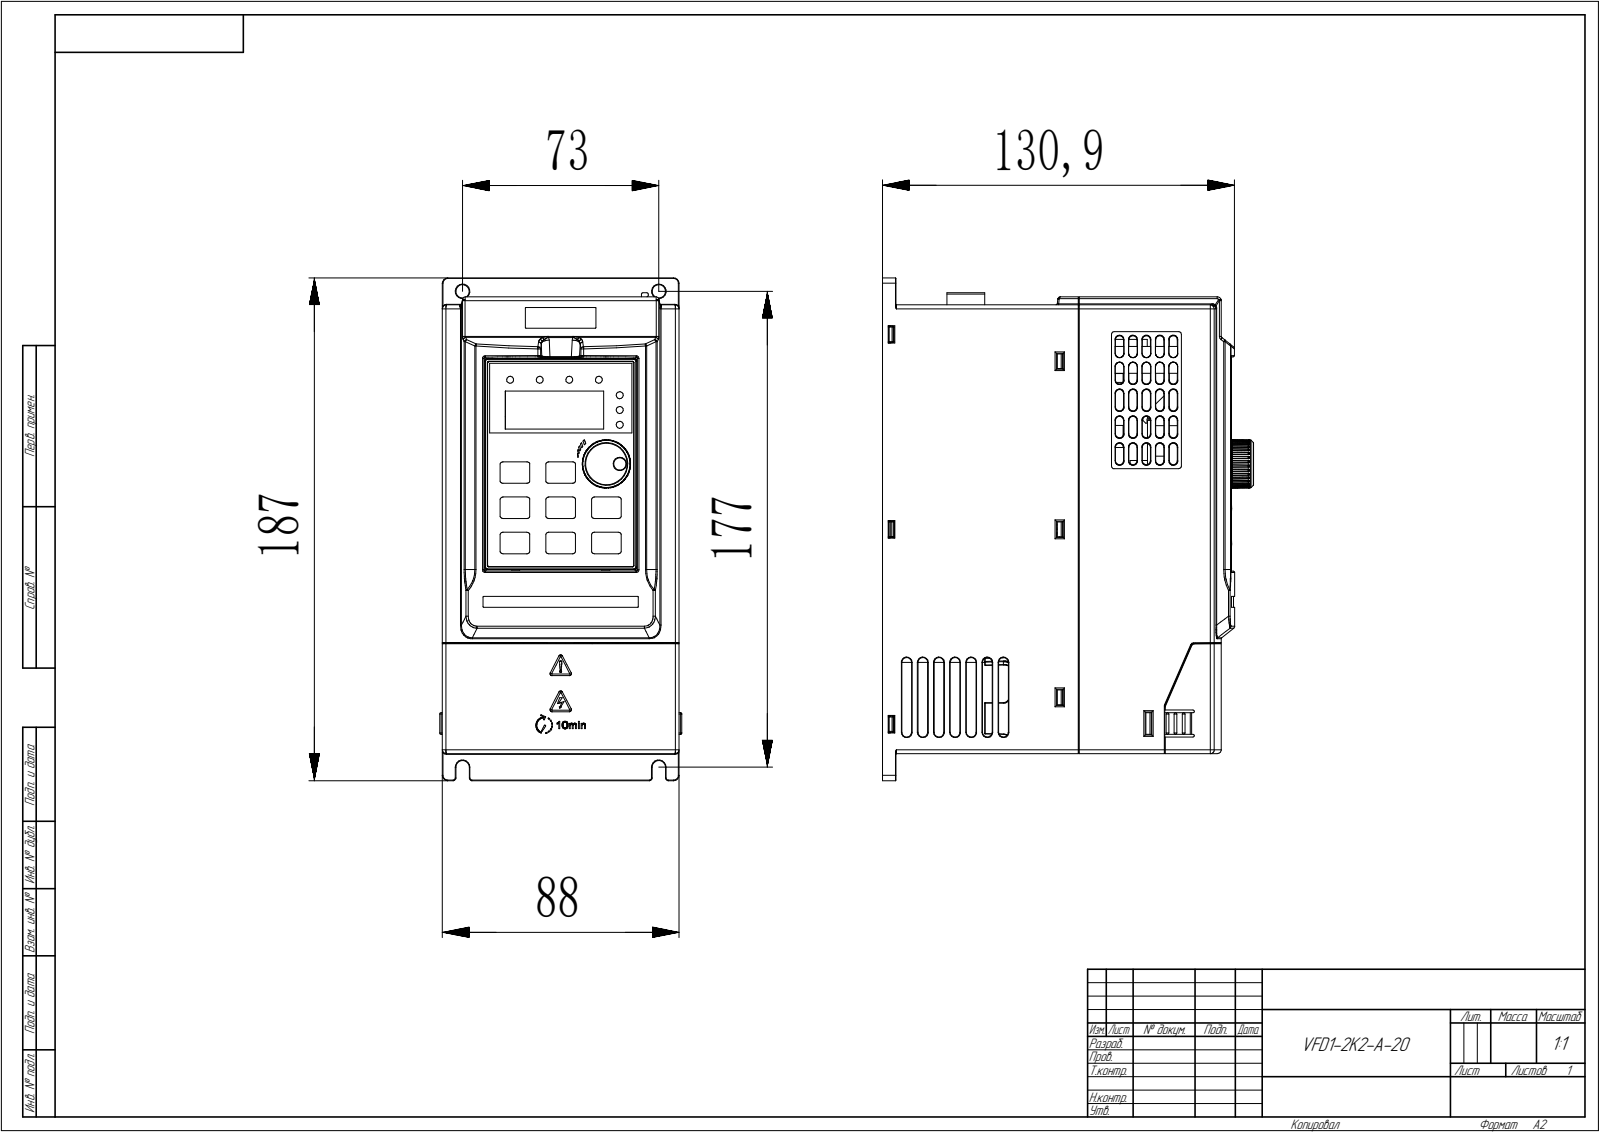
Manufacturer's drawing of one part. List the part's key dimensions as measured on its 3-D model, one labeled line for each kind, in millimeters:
Part name (STEP PRODUCT): FANXIA50-1_1_1; FANXIA50-1_1_2; FANXIA50-1_1_ASM; VM1000B-101-406_1 (+2 more)
STEP written by: CREO PARAMETRIC BY PTC INC, 2020074 (CONFIG_CONTROL_DESIGN)
Units: millimetres
Bodies: 2 solids, 7697 faces (4366 planar, 1895 cylindrical, 1436 other)
Overall size (bounding box): 187 × 138 × 90
Volume: 14 440 mm³ · Surface area: 381 416 mm²
Round holes (diameter × count): ⌀3.5 ×15, ⌀5 ×11, ⌀3 ×9, ⌀1.5 ×8, ⌀1.8 ×8, ⌀2.6 ×7, ⌀3.8 ×7, ⌀7 ×7, ⌀2.5 ×5, ⌀2 ×4, ⌀3.2 ×3, ⌀7.5 ×3
Round bosses / shafts (diameter × count): ⌀3 ×12, ⌀6 ×9, ⌀5 ×8, ⌀3.5 ×8, ⌀6.5 ×5, ⌀5.5 ×5, ⌀5.4 ×4, ⌀9.5 ×3
Partial cylindrical surfaces — rounded edges, fillets, slot ends (radius × count): R0.5 ×379, R0.2 ×152, R1 ×131, R0.3 ×123, R2 ×71, R2.5 ×36, R0.34 ×35, R1.5 ×13
Main face-to-face distances: 2, 88, 1.8, 0.64, 64.2, 66, 16, 60.4, 14.8, 66.2
Hole centre spacings: 21.46, 13.1, 17, 11, 28.28, 40, 31.23, 36.44
